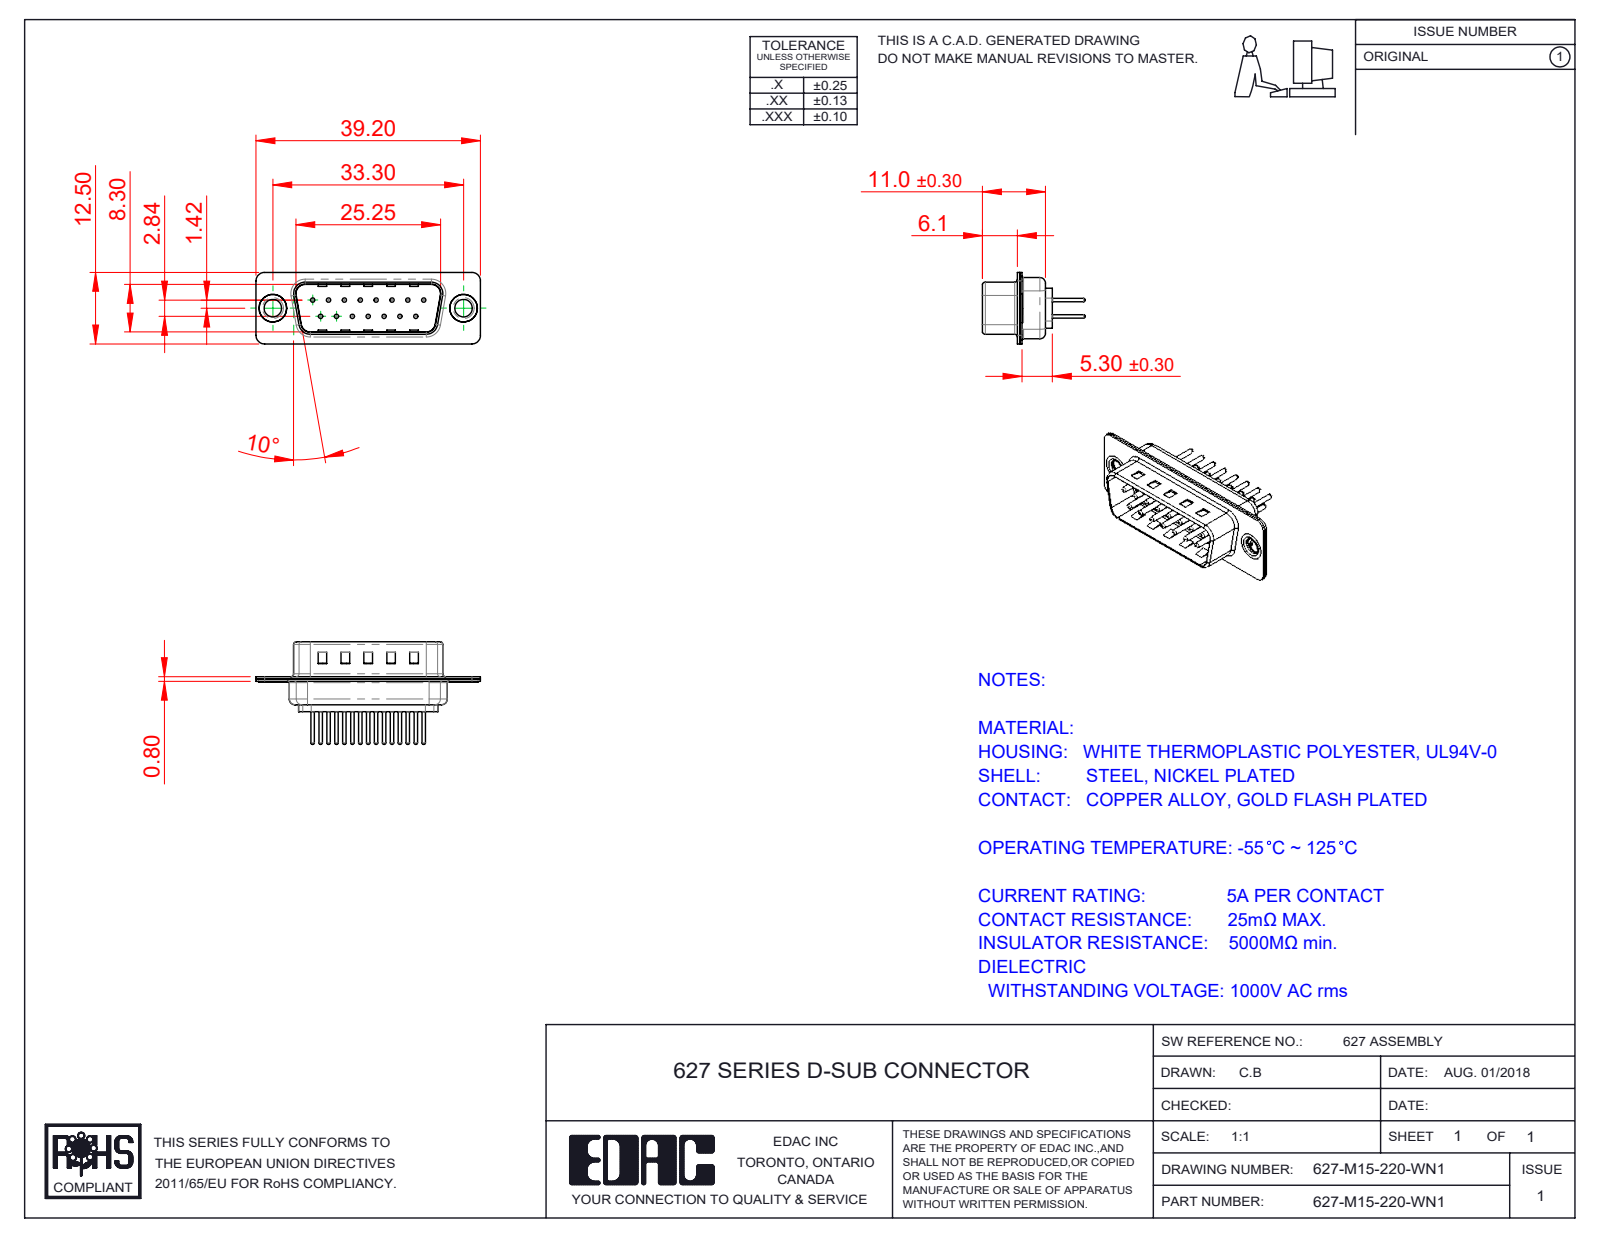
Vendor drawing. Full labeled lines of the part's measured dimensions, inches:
Part name (STEP PRODUCT): 627M Housing_15 Contacts; 627M Shell Front_15 Contacts; 627M Shell Rear_15 Contacts; 627M Contact Row 2_20 (+3 more)
STEP written by: SolidWorks 2020 (CONFIG_CONTROL_DESIGN)
Units: inches
Bodies: 20 solids, 869 faces (244 planar, 327 cylindrical, 298 other)
Overall size (bounding box): 1.543 × 0.705 × 0.492
Volume: 0.108 in³ · Surface area: 7.228 in²
Round holes (diameter × count): ⌀0.03 ×15, ⌀0.063 ×15, ⌀0.079 ×15, ⌀0.12 ×2, ⌀0.157 ×2, ⌀0.189 ×2
Round bosses / shafts (diameter × count): ⌀0.059 ×15, ⌀0.024 ×15, ⌀0.197 ×2, ⌀0.193 ×2, ⌀0.14 ×2
Partial cylindrical surfaces — rounded edges, fillets, slot ends (radius × count): R0.059 ×16, R0.079 ×12, R0.02 ×8, R0.063 ×8, R0.01 ×4, R0.024 ×4, R0.026 ×4, R0.035 ×4
Main face-to-face distances: 0.016, 0.031, 0.374, 0.358, 0.343, 0.39, 0.047, 0.24, 0.224, 0.209
Hole centre spacings: 0.124, 0.109, 0.218, 0.327, 0.436, 0.198, 0.198, 0.294
